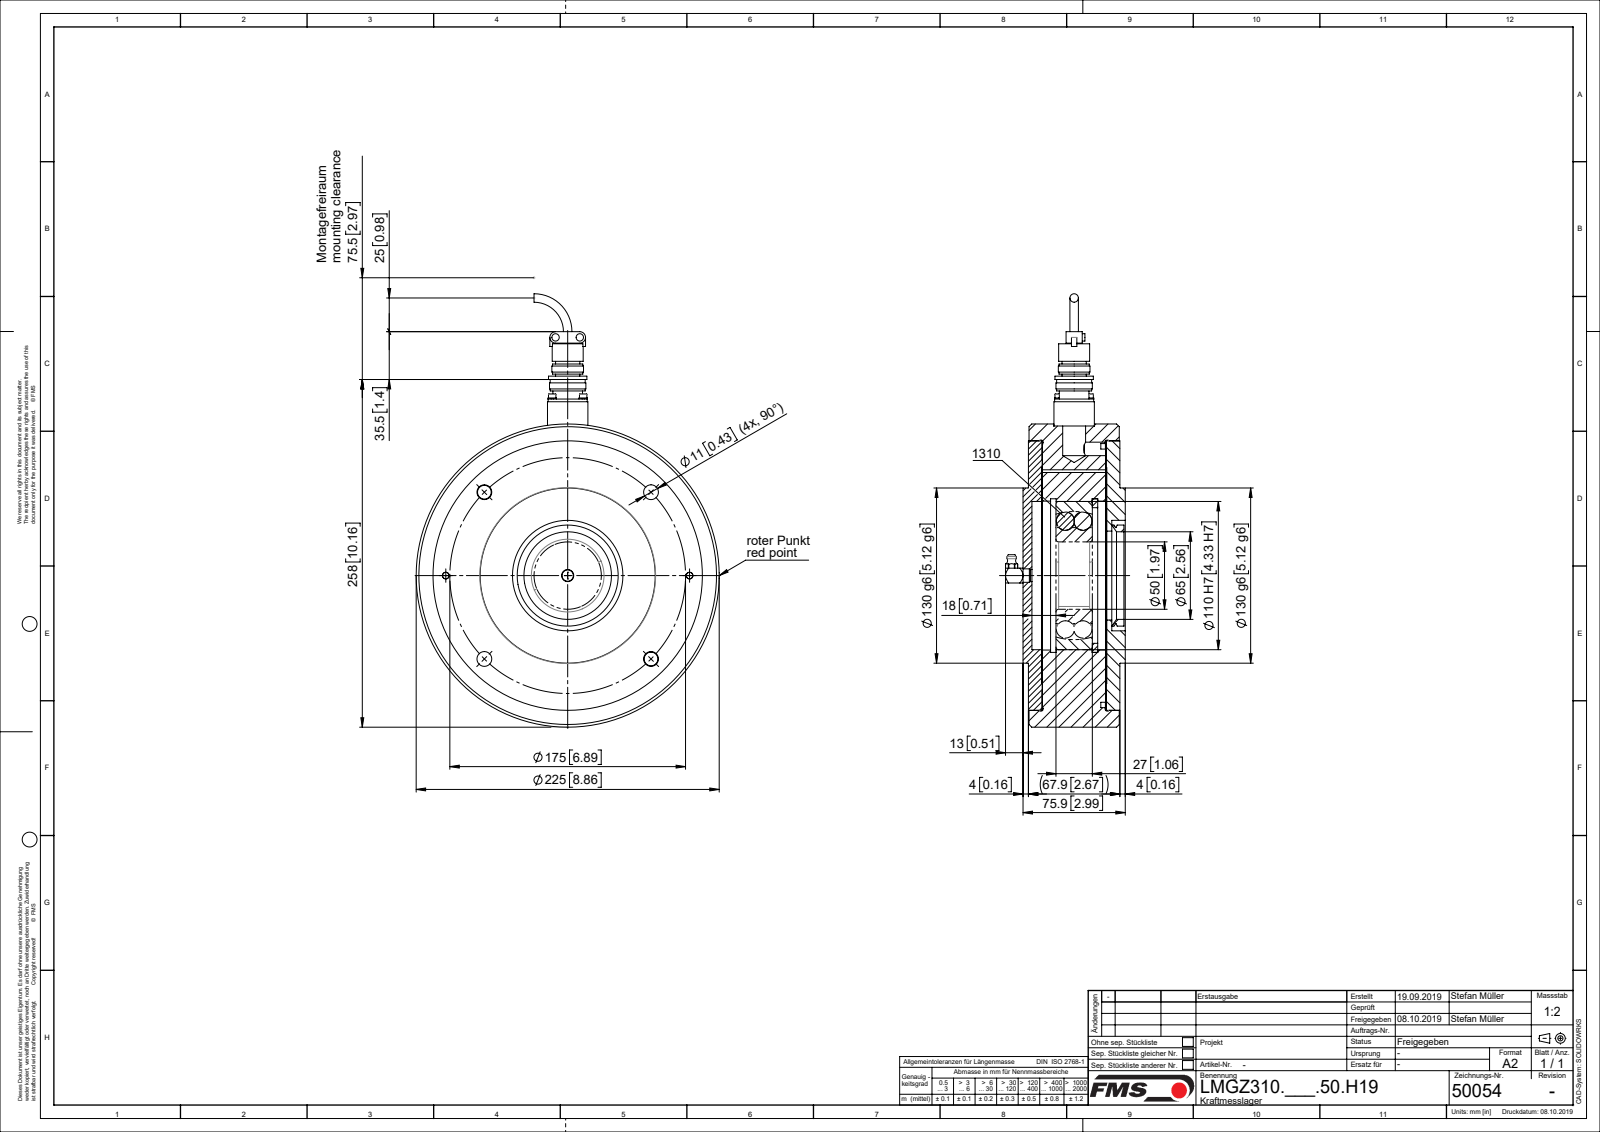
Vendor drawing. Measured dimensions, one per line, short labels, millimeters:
name: L50054; L4765504; TEIL1; L49152 (+8 more)
written by: Mechanical Desktop 2007 (CONFIG_CONTROL_DESIGN)
unit: mm
bodies: 21 solids, 426 faces (122 planar, 238 cylindrical, 66 other)
size: 321.65 × 225 × 126.8
volume: 2 407 000 mm³; area: 392 190 mm²
holes: 6× ⌀11, 4× ⌀2.6, 4× ⌀3.2, 4× ⌀3.4, 4× ⌀9, 2× ⌀5, 2× ⌀6.6, 1× ⌀8.68, 1× ⌀23, 1× ⌀50, 1× ⌀64, 1× ⌀66
bosses: 6× ⌀5.5, 4× ⌀6.2, 4× ⌀3, 4× ⌀2.5, 3× ⌀10, 2× ⌀6, 1× ⌀225, 1× ⌀199
rounds: 2× R4.25, 1× R81, 1× R86
face distances: 9.7, 47.25, 10.45, 10.75, 47.45, 10.2, 57.45, 57.7, 47, 10
hole spacings: 16.26, 23, 68.17, 87.5, 123.74, 164.45, 32.53, 90.5
